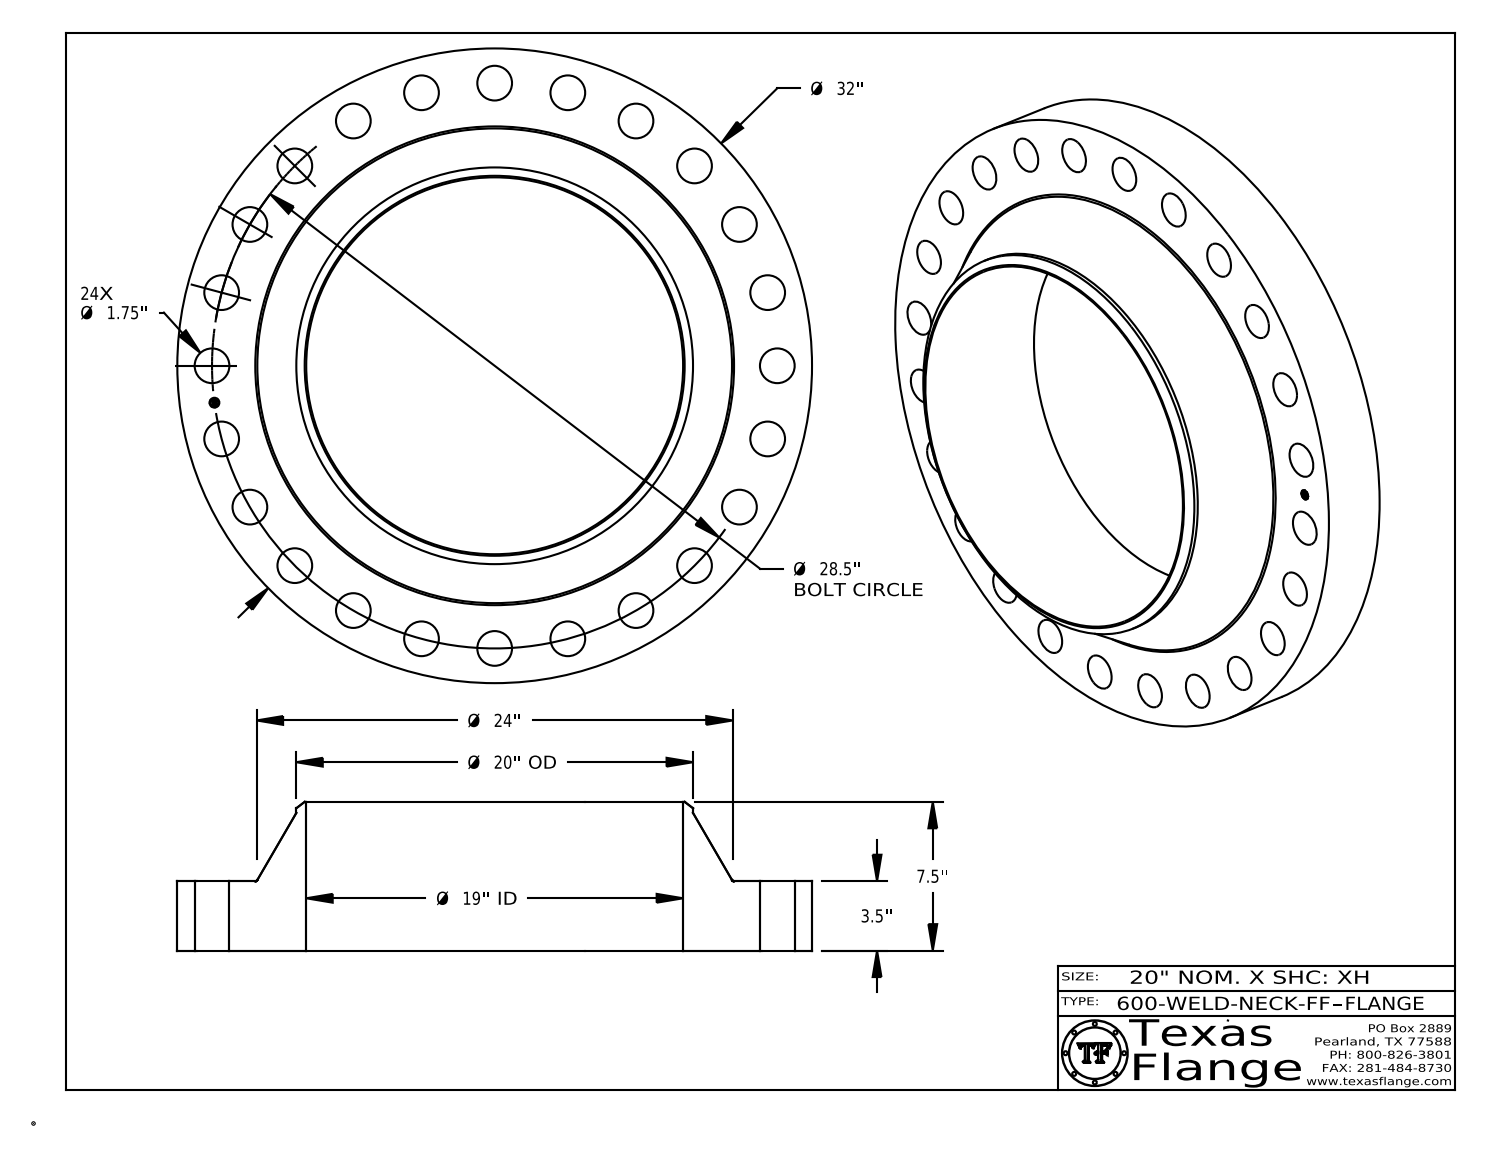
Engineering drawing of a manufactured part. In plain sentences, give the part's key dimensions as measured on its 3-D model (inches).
The part is named "600-WELD-NECK-FF". Its 3-D file was written by "CATIA V5 STEP AP214 (AUTOMOTIVE_DESIGN)". It is 1 solid with 448 faces: 368 planar, 74 cylindrical and 6 other. Overall it measures 32 by 32 by 7.5 inches. Its volume is 1 969 cubic inches and its surface area 2 345 square inches. Round holes: 24 of diameter 1.75, 1 of diameter 0.495, 1 of diameter 19. Round bosses or shafts: 8 of diameter 0.03, 1 of diameter 32, 1 of diameter 20, 1 of diameter 0.39. The main face-to-face distances are 3.5, 7.5, 4, 0.015, 3.485, 4.015, 0.148, 0.145, 0.027, 0.096. The hole center spacings are 14.25, 3.72, 7.376, 24.682, 26.331, 27.529, 20.153, 10.907.
